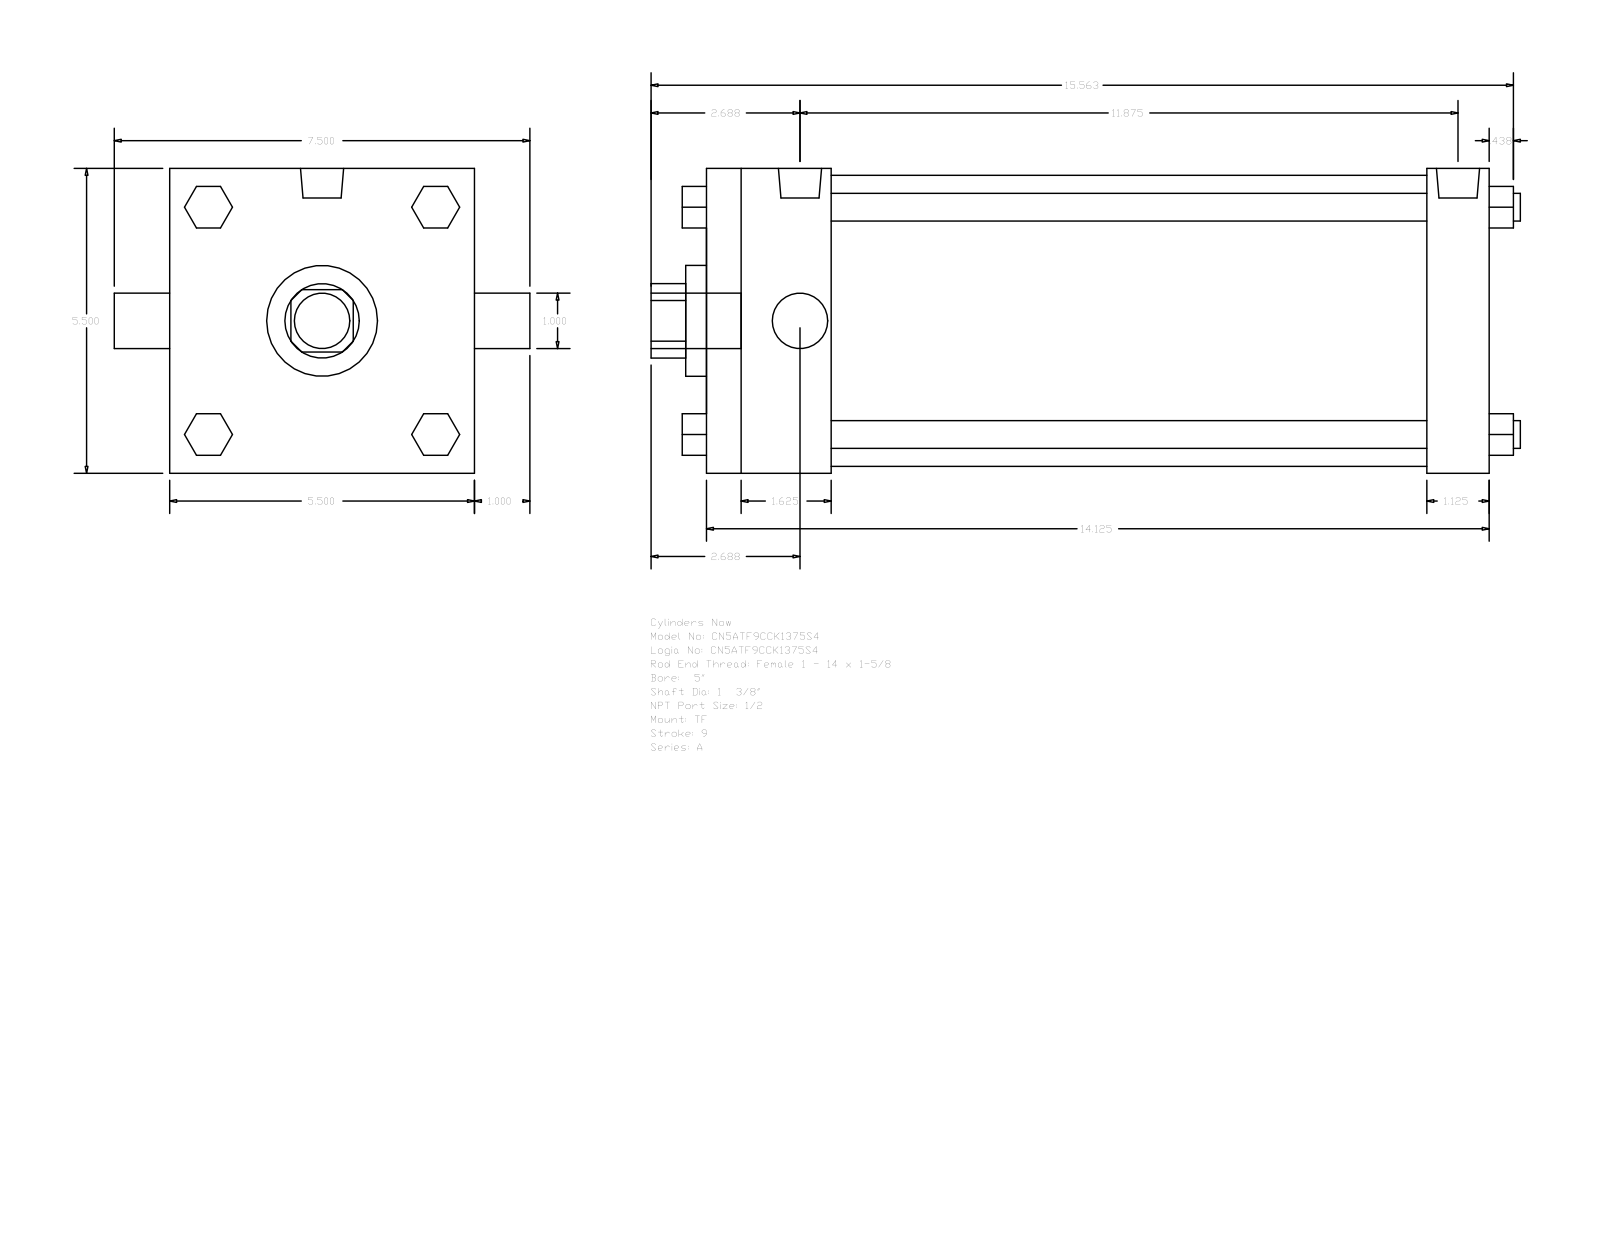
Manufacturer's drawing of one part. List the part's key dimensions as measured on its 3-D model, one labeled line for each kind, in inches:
Part name (STEP PRODUCT): A_TF__0500_1.375
STEP written by: GSSL Pune (CONFIG_CONTROL_DESIGN)
Units: inches
Bodies: 0 solids, 120 faces (92 planar, 28 cylindrical, 0 other)
Overall size (bounding box): 15.687 × 7.5 × 5.5
Round holes (diameter × count): ⌀1 ×1, ⌀1.375 ×1, ⌀2 ×1, ⌀5.25 ×1
Round bosses / shafts (diameter × count): ⌀0.5 ×4, ⌀0.344 ×3, ⌀0.778 ×2, ⌀1 ×1
Partial cylindrical surfaces — rounded edges, fillets, slot ends (radius × count): R0.672 ×1
Main face-to-face distances: 5.5, 14.125, 1.125, 13, 2.25, 10.75, 11.875, 0.75, 2.05, 3.55
